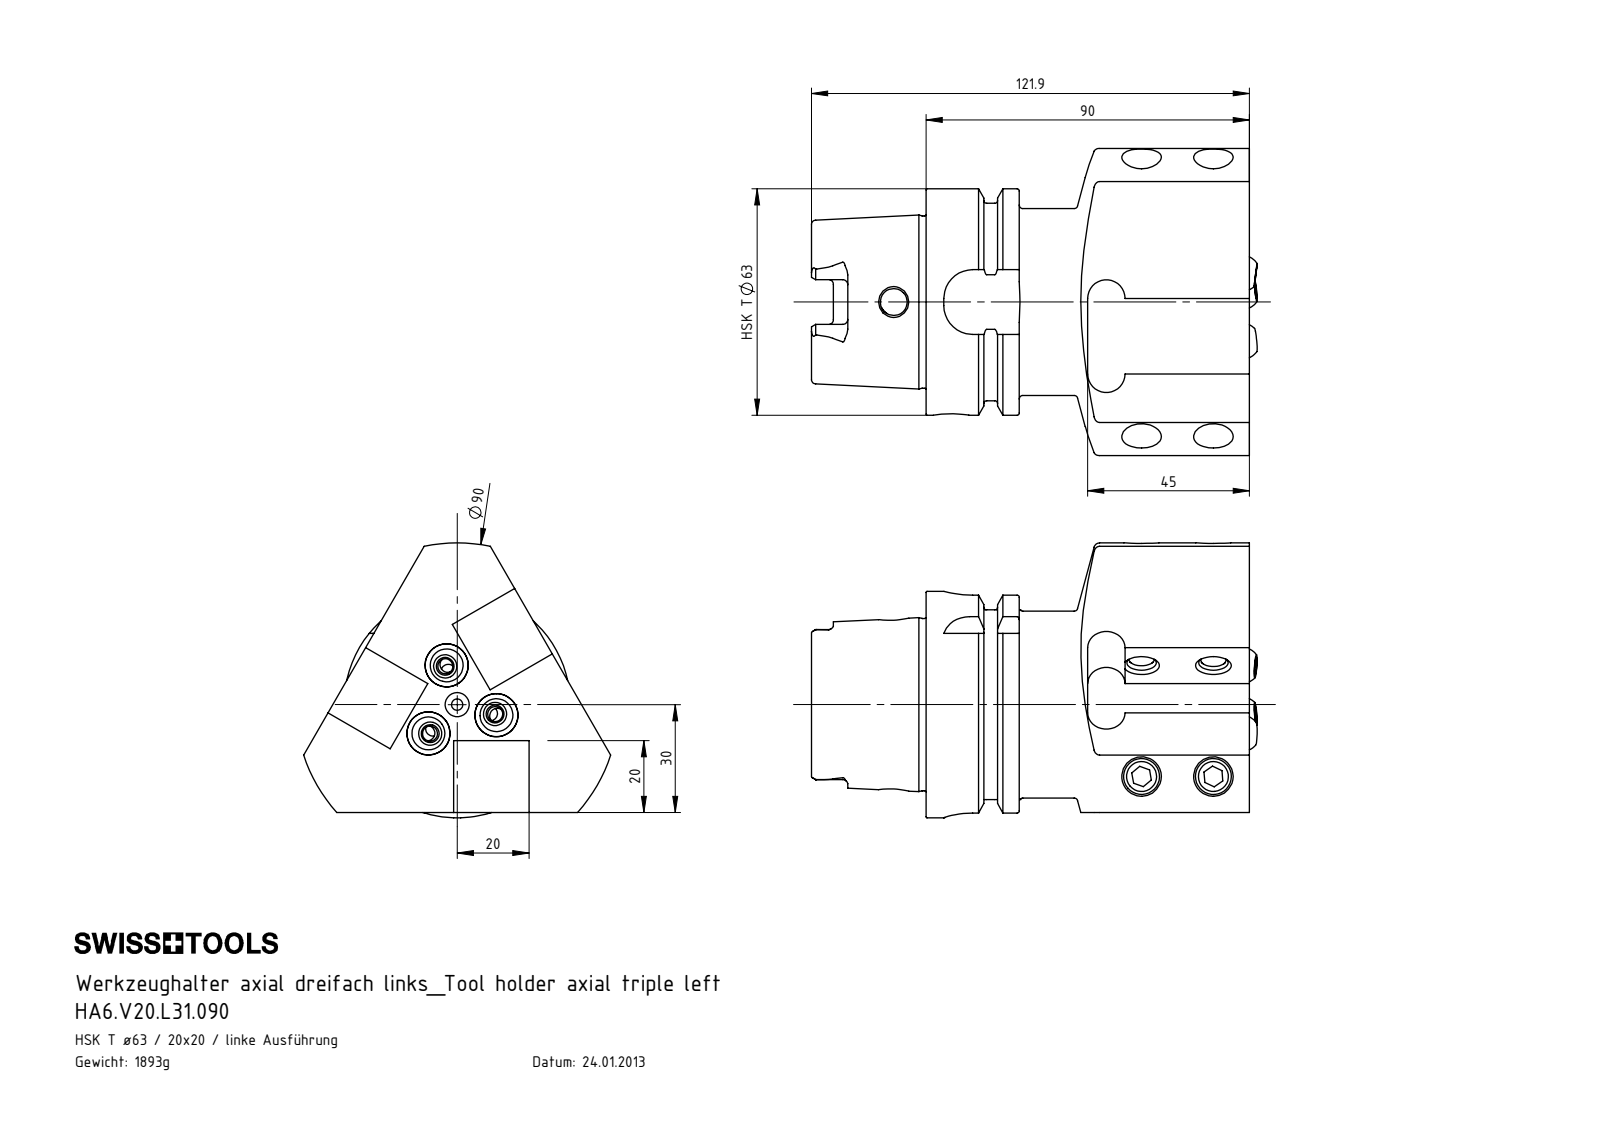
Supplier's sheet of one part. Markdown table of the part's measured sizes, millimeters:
| quantity | value |
| --- | --- |
| part name | KU1-U12.001.010_2; HA6.V20.L31.090; KU1-U12.001.010; KU1-U12.001.010_1 (+2 more) |
| STEP written by | SolidWorks 2022 (CONFIG_CONTROL_DESIGN) |
| units | millimeters |
| bodies | 13 solids, 392 faces (124 planar, 124 cylindrical, 144 other) |
| overall size | 123.7 × 85.5 × 76.5 |
| volume | 242 058 mm³ |
| surface area | 63 728 mm² |
| round holes (diameter × count) | 4.2 × 6, 8.2 × 6, 11 × 6, 7 × 3, 12 × 3, 3.15 × 1, 7.5 × 1, 8.4 × 1, 10 × 1, 17 × 1, 19 × 1, 34 × 1 |
| round bosses / shafts (diameter × count) | 10 × 6, 63 × 1, 54.95 × 1, 52 × 1, 47.94 × 1 |
| partial cylindrical surfaces (radius × count) | 1.4 × 6, 5.2 × 6, 2.88 × 4, 8 × 4, 45 × 1 |
| main face-to-face distances | 20, 45, 21, 90, 25.95, 19.05, 64.05, 16, 8, 9.95 |
| hole center spacings | 19.6, 20, 11.32, 11.31, 56.65, 75.69 |
